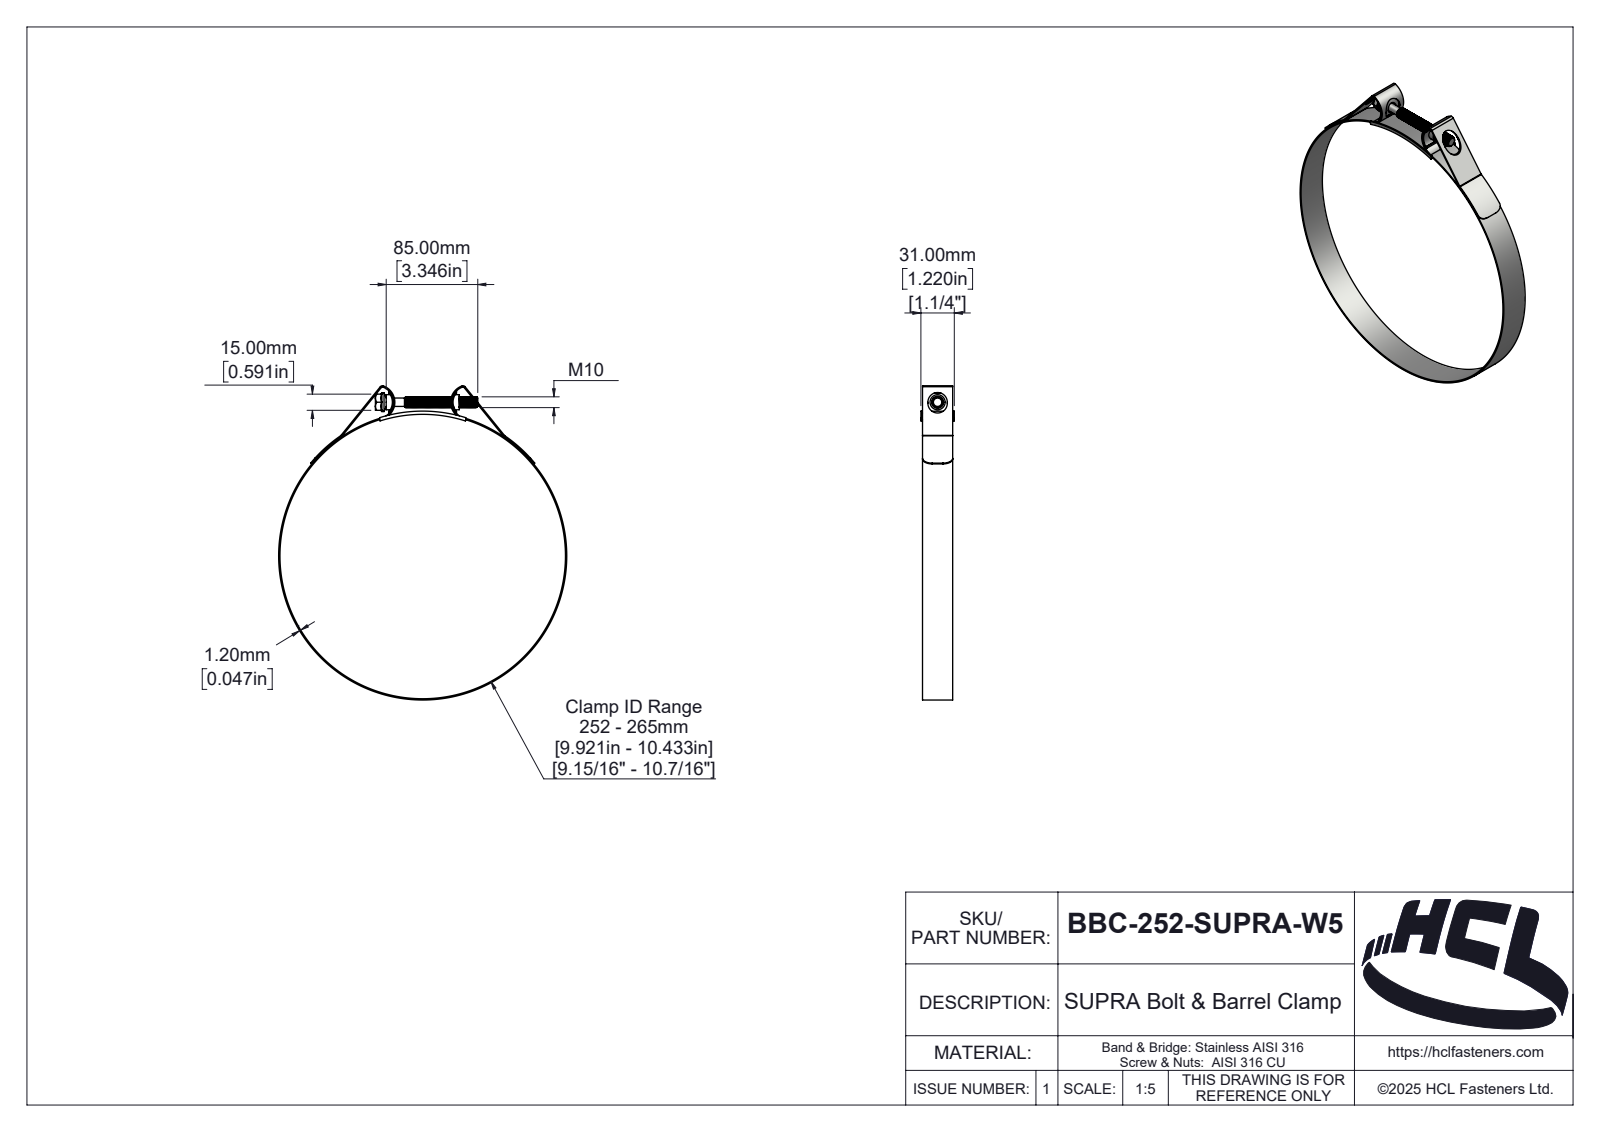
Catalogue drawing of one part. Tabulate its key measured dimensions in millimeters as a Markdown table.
| quantity | value |
| --- | --- |
| part name | BBC-252-SUPRA-W5 |
| STEP written by | SolidWorks 2025 (AUTOMOTIVE_DESIGN) |
| units | millimeters |
| bodies | 5 solids, 382 faces (50 planar, 245 cylindrical, 87 other) |
| overall size | 291.54 × 267.4 × 31 |
| volume | 45 889 mm³ |
| surface area | 71 736 mm² |
| round holes (diameter × count) | 265 × 1 |
| round bosses / shafts (diameter × count) | 267.4 × 1, 17.32 × 1, 14 × 1, 10 × 1, 7.8 × 1 |
| partial cylindrical surfaces (radius × count) | 1 × 4, 1.3 × 2, 2 × 2, 2.5 × 2, 3.2 × 2, 9 × 2, 13.78 × 2, 14.78 × 2 |
| main face-to-face distances | 1.2, 28, 1.5, 29.5, 29.8, 28.3, 31, 28.6, 15, 2.5 |
